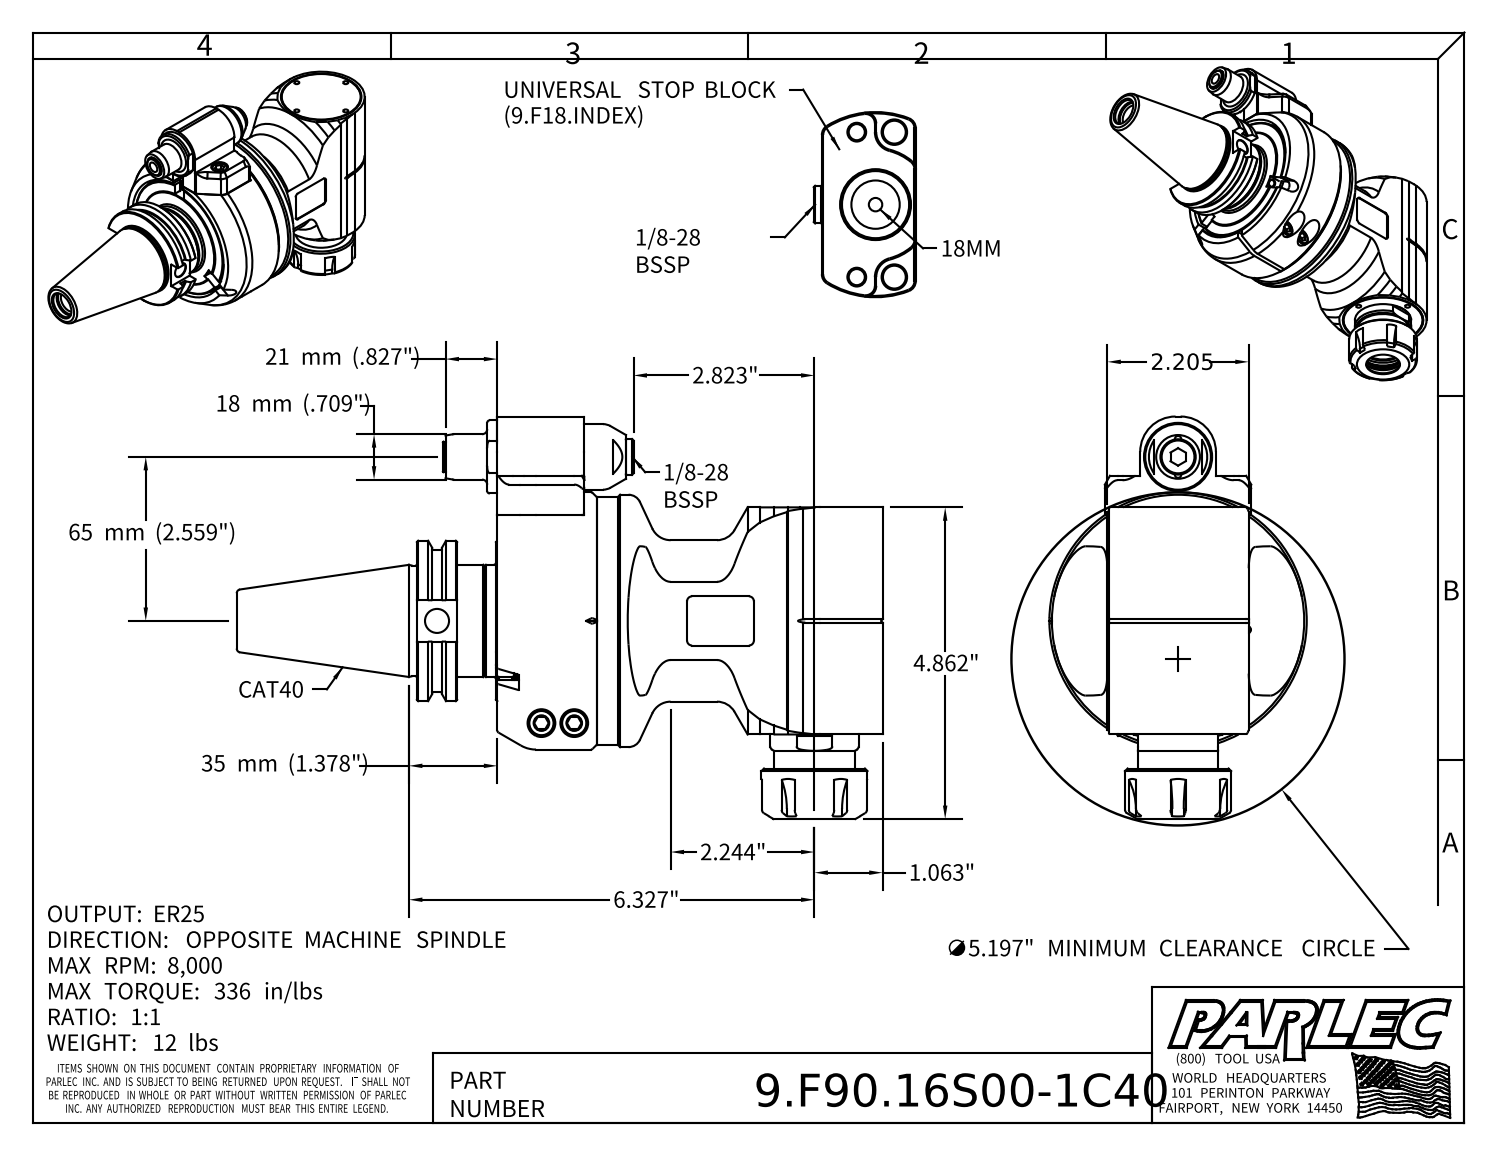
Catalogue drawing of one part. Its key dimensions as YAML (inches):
part_name: "9.F90.16S00-1C40; 9_F90_16S00; 9_GA1_446_2 (EVO, Type 1, C40, 65mm, 35mm)"
step_written_by: "Autodesk Inventor 2022 (AUTOMOTIVE_DESIGN)"
units: inches
bodies: {solids: 4, faces: 645, planar: 282, cylindrical: 169, other: 194}
overall_size: [10.077, 6.28, 4.016]
volume: 60.35
surface_area: 221.3
round_holes:
  - {diameter: 0.126, count: 8}
  - {diameter: 0.197, count: 3}
  - {diameter: 0.256, count: 3}
  - {diameter: 0.102, count: 2}
  - {diameter: 0.13, count: 2}
  - {diameter: 0.165, count: 2}
  - {diameter: 0.315, count: 2}
  - {diameter: 0.409, count: 2}
  - {diameter: 0.433, count: 2}
  - {diameter: 0.492, count: 2}
  - {diameter: 1.063, count: 2}
  - {diameter: 0.098, count: 1}
round_bosses_or_shafts:
  - {diameter: 0.394, count: 4}
  - {diameter: 0.709, count: 2}
  - {diameter: 0.472, count: 2}
  - {diameter: 0.315, count: 2}
  - {diameter: 0.236, count: 2}
  - {diameter: 0.098, count: 2}
  - {diameter: 4.016, count: 1}
  - {diameter: 3.937, count: 1}
partial_cylinders:
  - {radius: 0.039, count: 14}
  - {radius: 0.079, count: 12}
  - {radius: 0.118, count: 6}
  - {radius: 0.984, count: 6}
  - {radius: 0.157, count: 4}
  - {radius: 0.016, count: 2}
  - {radius: 0.02, count: 2}
  - {radius: 0.315, count: 2}
face_to_face_distances: [0.276, 0.02, 1.252, 0.335, 1.555, 1.28, 1.299, 0.059, 0.303, 1.22]
hole_center_spacings: [0.325, 0.459, 0.846, 1.197, 0.276, 0.504, 0.65, 0.74]
